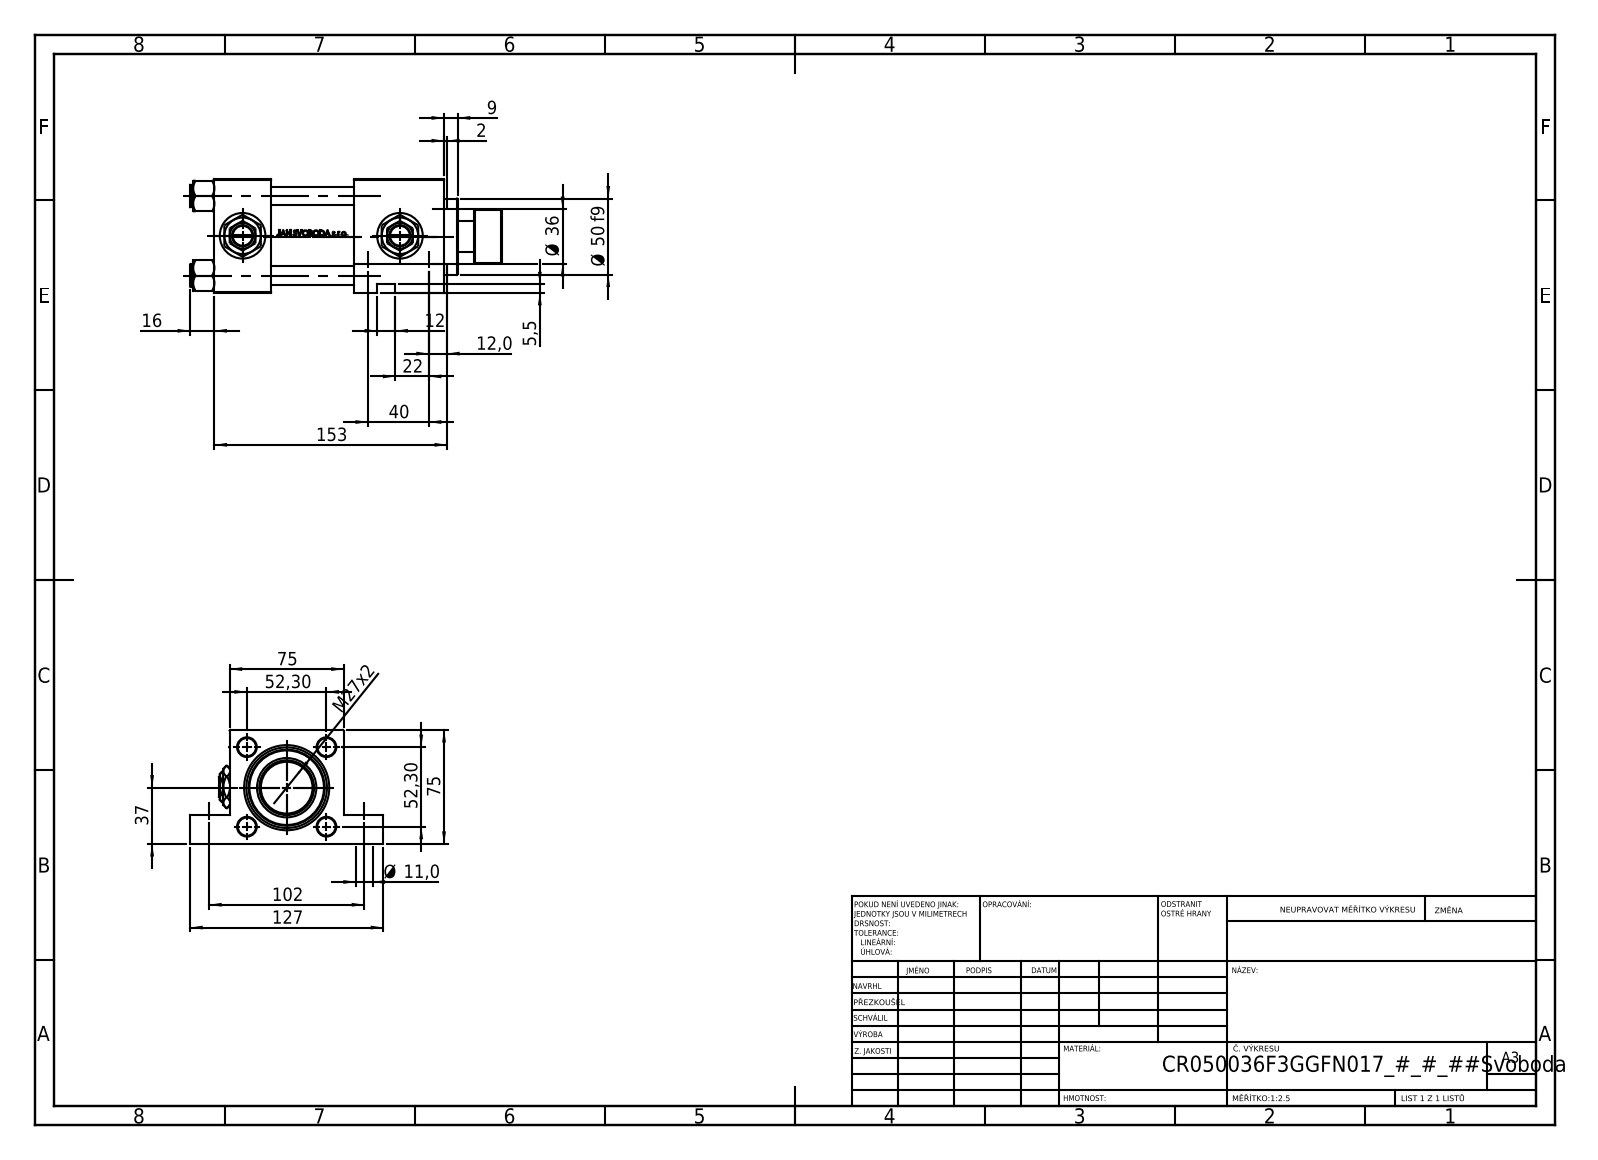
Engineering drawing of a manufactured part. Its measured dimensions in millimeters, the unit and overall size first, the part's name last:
Units: millimetres
Overall size (bounding box): 205 × 127 × 75
Round holes (diameter × count): ⌀12 ×4, ⌀20.96 ×4, ⌀30 ×4, ⌀7 ×3, ⌀11 ×2, ⌀11 ×2, ⌀25.5 ×1, ⌀36 ×1, ⌀39 ×1, ⌀41 ×1, ⌀53 ×1
Round bosses / shafts (diameter × count): ⌀15 ×4, ⌀56 ×1, ⌀50 ×1, ⌀35 ×1, ⌀21 ×1
Main face-to-face distances: 75, 37, 55, 92, 59, 151, 114, 19, 56, 74.8
Hole centre spacings: 52.3, 36.63, 37.34, 40, 51.62, 60.21, 73.96, 96.99
Volume: 713 827 mm³ · Surface area: 169 664 mm²
Bodies: 14 solids, 1216 faces (488 planar, 140 cylindrical, 588 other)
Part name (STEP PRODUCT): V215_VC_A; Zatka_pro_OIL_PORT; NUT_M5_F; V215CR_F_Body (+3 more)
STEP written by: SolidWorks 2019 (CONFIG_CONTROL_DESIGN)
